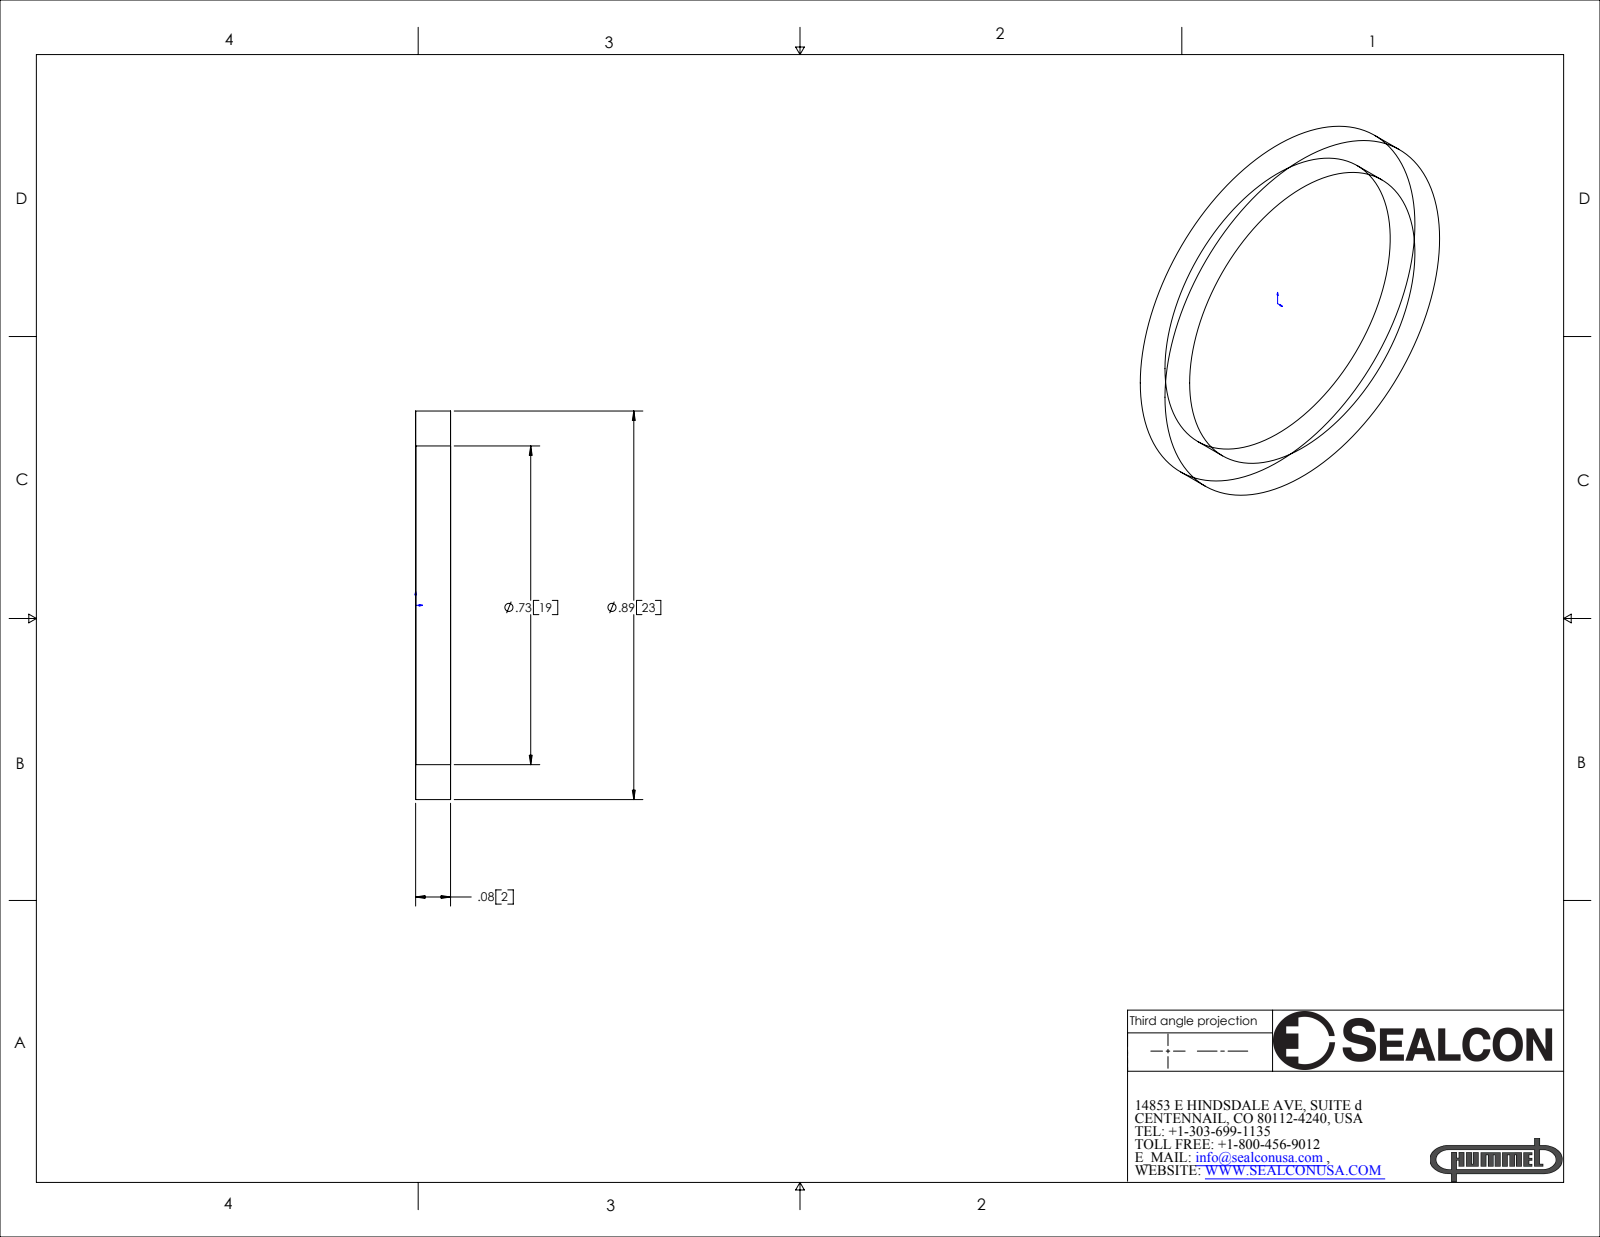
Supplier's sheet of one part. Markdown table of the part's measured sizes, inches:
| quantity | value |
| --- | --- |
| part name | SR-11-NY |
| STEP written by | SolidWorks 2007 (CONFIG_CONTROL_DESIGN) |
| units | inches |
| bodies | 1 solid, 6 faces (2 planar, 4 cylindrical, 0 other) |
| overall size | 0.89 × 0.89 × 0.08 |
| volume | 0.016 in³ |
| surface area | 0.814 in² |
| round holes (diameter × count) | 0.73 × 1 |
| round bosses / shafts (diameter × count) | 0.89 × 1 |
| main face-to-face distances | 0.08 |
